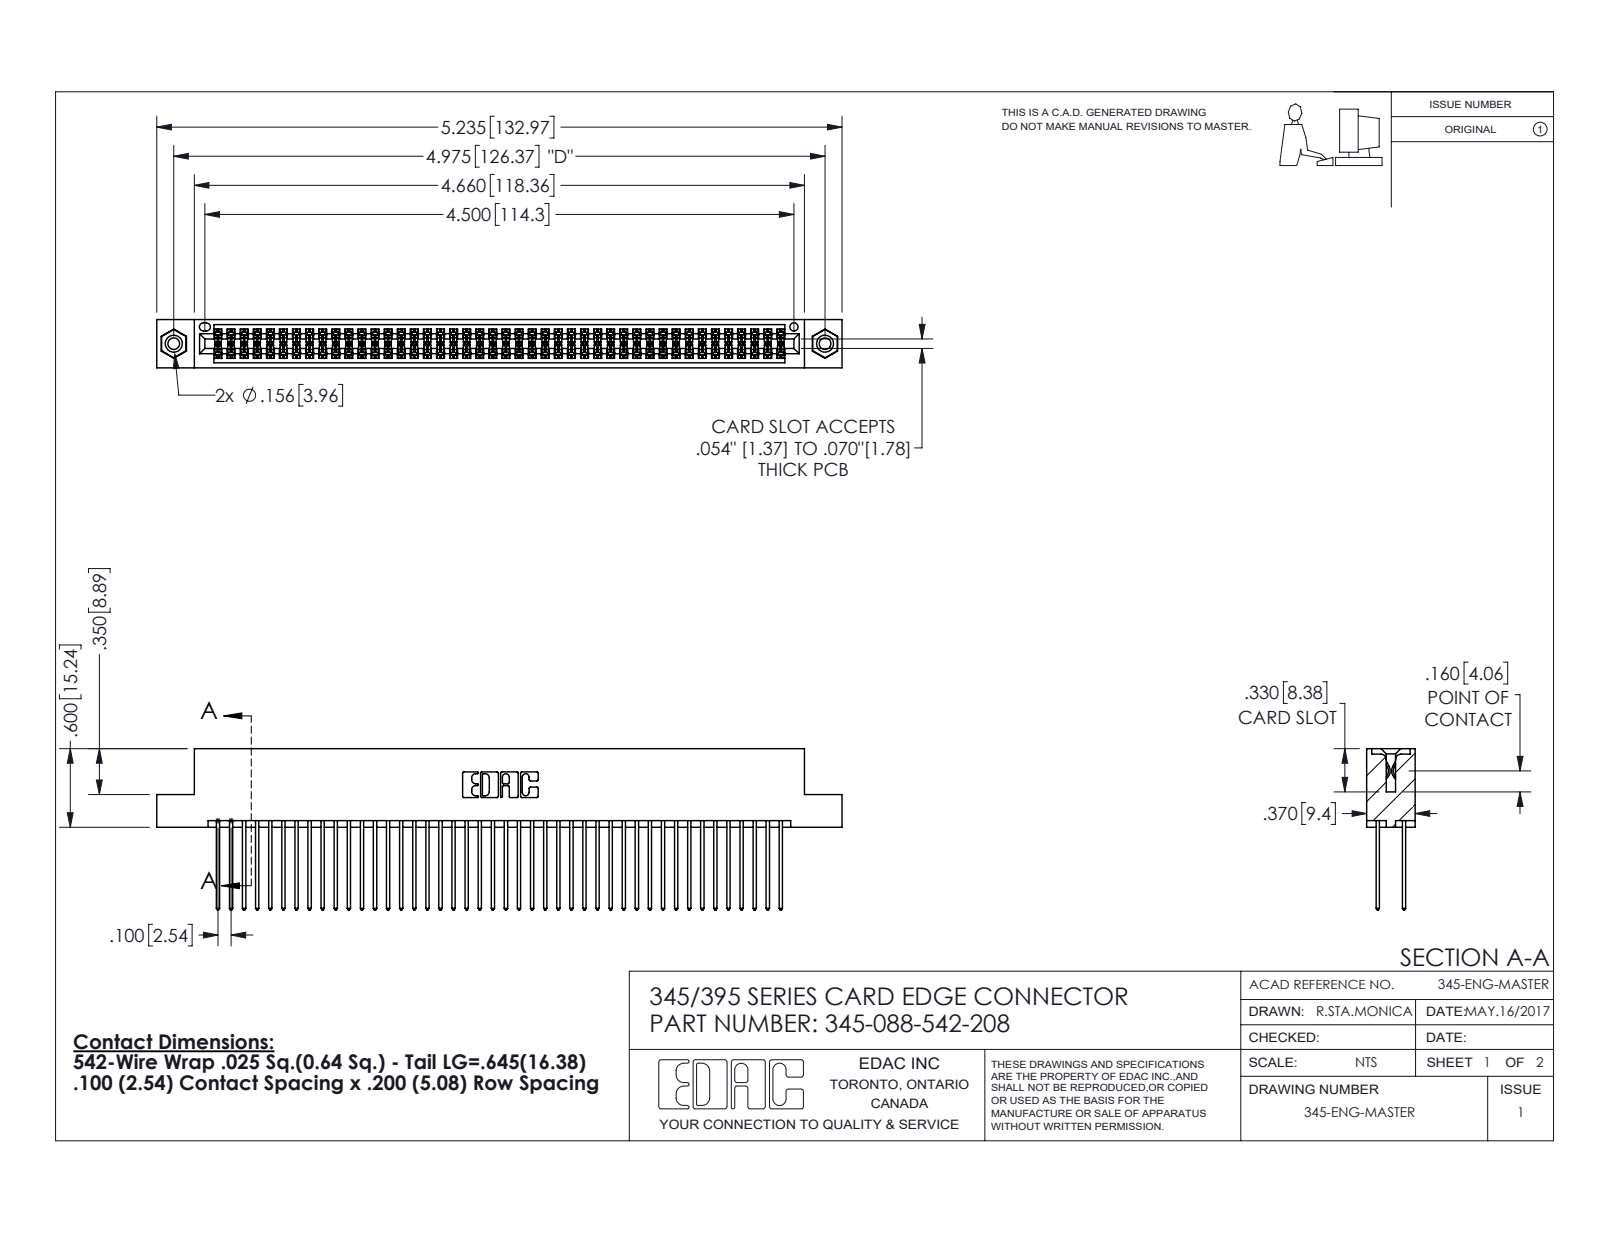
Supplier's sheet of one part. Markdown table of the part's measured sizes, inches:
| quantity | value |
| --- | --- |
| part name | 345-250-001_345-250-003-102; 345-292-001_345-293-142; 345-088-542-208; 345 Part_Flush Mounting Lugs - 0.156 Dia-TI |
| STEP written by | SolidWorks 2016 (CONFIG_CONTROL_DESIGN) |
| units | inches |
| bodies | 91 solids, 4586 faces (3016 planar, 1554 cylindrical, 16 other) |
| overall size | 5.235 × 1.232 × 0.37 |
| volume | 0.814 in³ |
| surface area | 33.61 in² |
| round holes (diameter × count) | 0.089 × 2, 0.125 × 2, 0.156 × 2, 0.064 × 1 |
| round bosses / shafts (diameter × count) | 0.155 × 2 |
| partial cylindrical surfaces (radius × count) | 0.006 × 132, 0.01 × 88, 0.01 × 22, 0.007 × 6, 0.031 × 6, 0.026 × 3, 0.014 × 2, 0.019 × 2 |
| main face-to-face distances | 0.072, 0.298, 0.2, 0.098, 0.272, 0.025, 0.225, 0.37, 0.175, 0.149 |
| hole center spacings | 0.27, 4.739, 4.975 |
